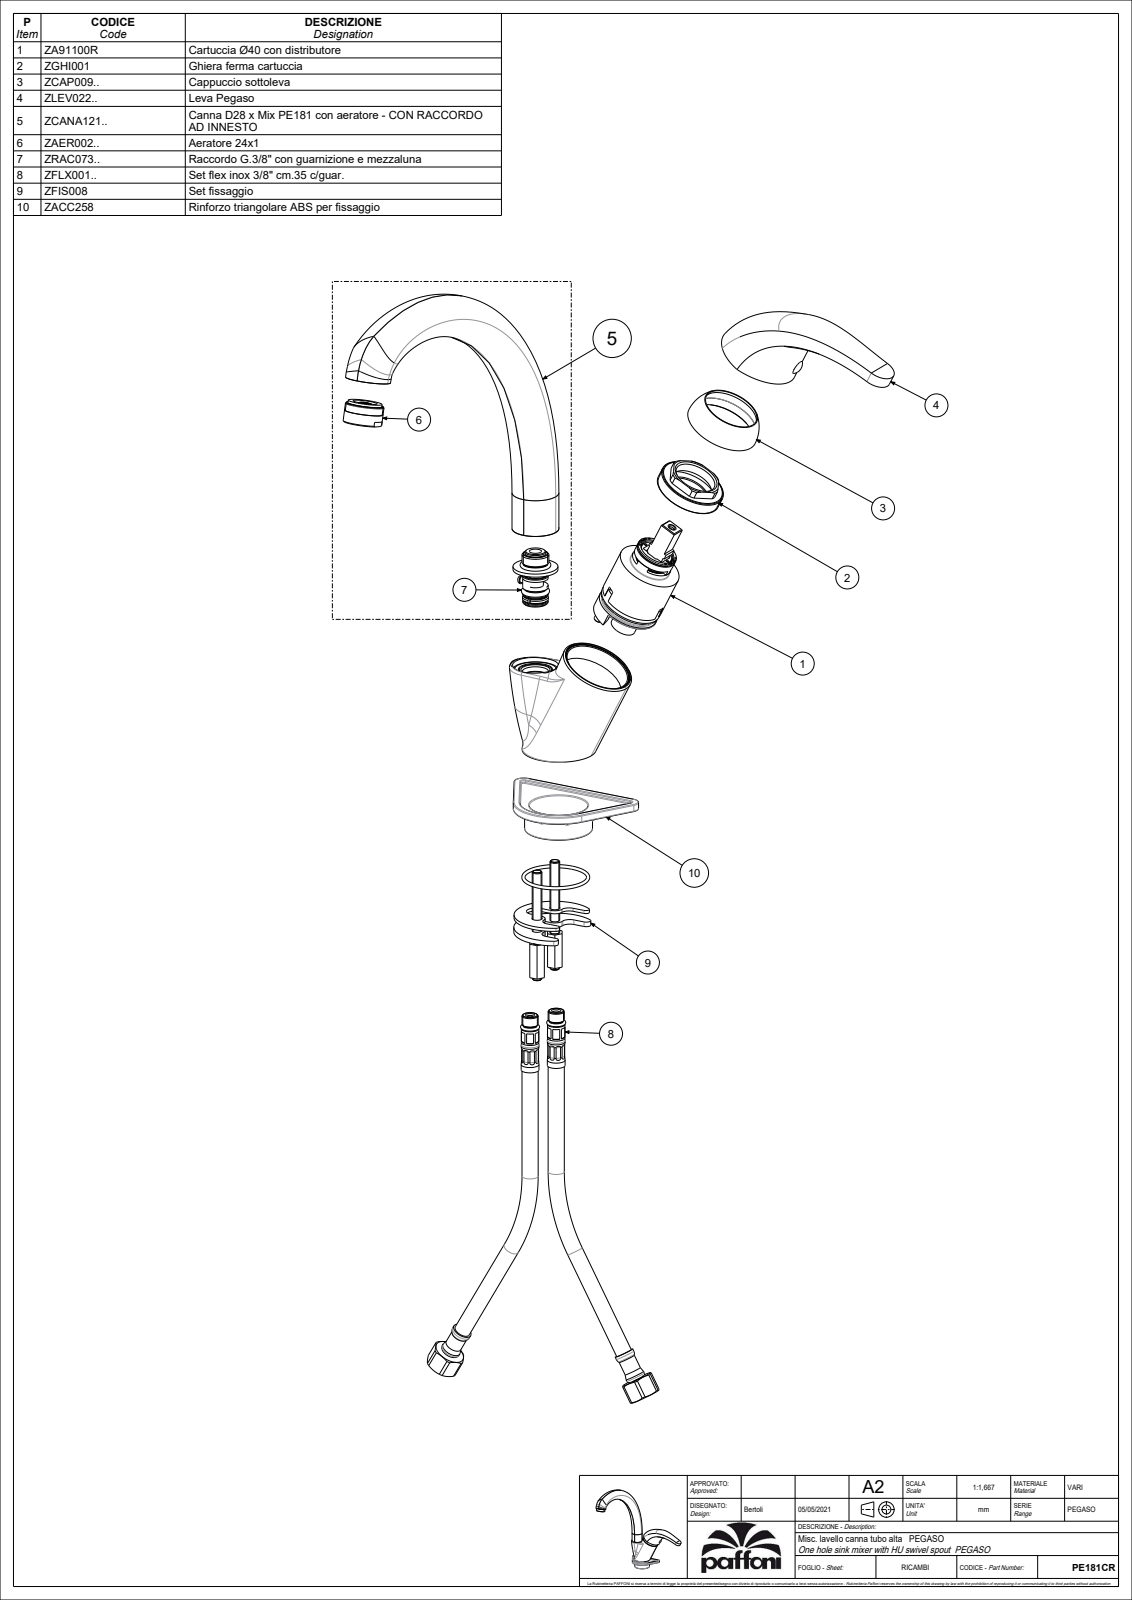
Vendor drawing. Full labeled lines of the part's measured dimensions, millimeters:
Part name (STEP PRODUCT): PE181CR_SW0001
STEP written by: CREO PARAMETRIC BY PTC INC, 2022124 (CONFIG_CONTROL_DESIGN)
Units: millimetres
Bodies: 2 solids, 1162 faces (932 planar, 90 cylindrical, 140 other)
Overall size (bounding box): 247.52 × 246.21 × 159.43
Volume: 150 744 mm³ · Surface area: 104 996 mm²
Round holes (diameter × count): ⌀5.5 ×3, ⌀8 ×3, ⌀6 ×2, ⌀9 ×2, ⌀11 ×2, ⌀17 ×2, ⌀4 ×1, ⌀15 ×1, ⌀16 ×1, ⌀16.5 ×1, ⌀18.2 ×1, ⌀20 ×1
Round bosses / shafts (diameter × count): ⌀24 ×1, ⌀20 ×1, ⌀19.5 ×1, ⌀18.8 ×1, ⌀8 ×1, ⌀5 ×1
Partial cylindrical surfaces — rounded edges, fillets, slot ends (radius × count): R1 ×8, R3.9 ×1, R15.5 ×1
Main face-to-face distances: 46.5, 3, 61, 14.5, 1.5, 84.22, 37.72, 23.22, 4.5, 7
Hole centre spacings: 8.6, 15.62, 15.81, 21.83, 24.2, 14, 15, 24
